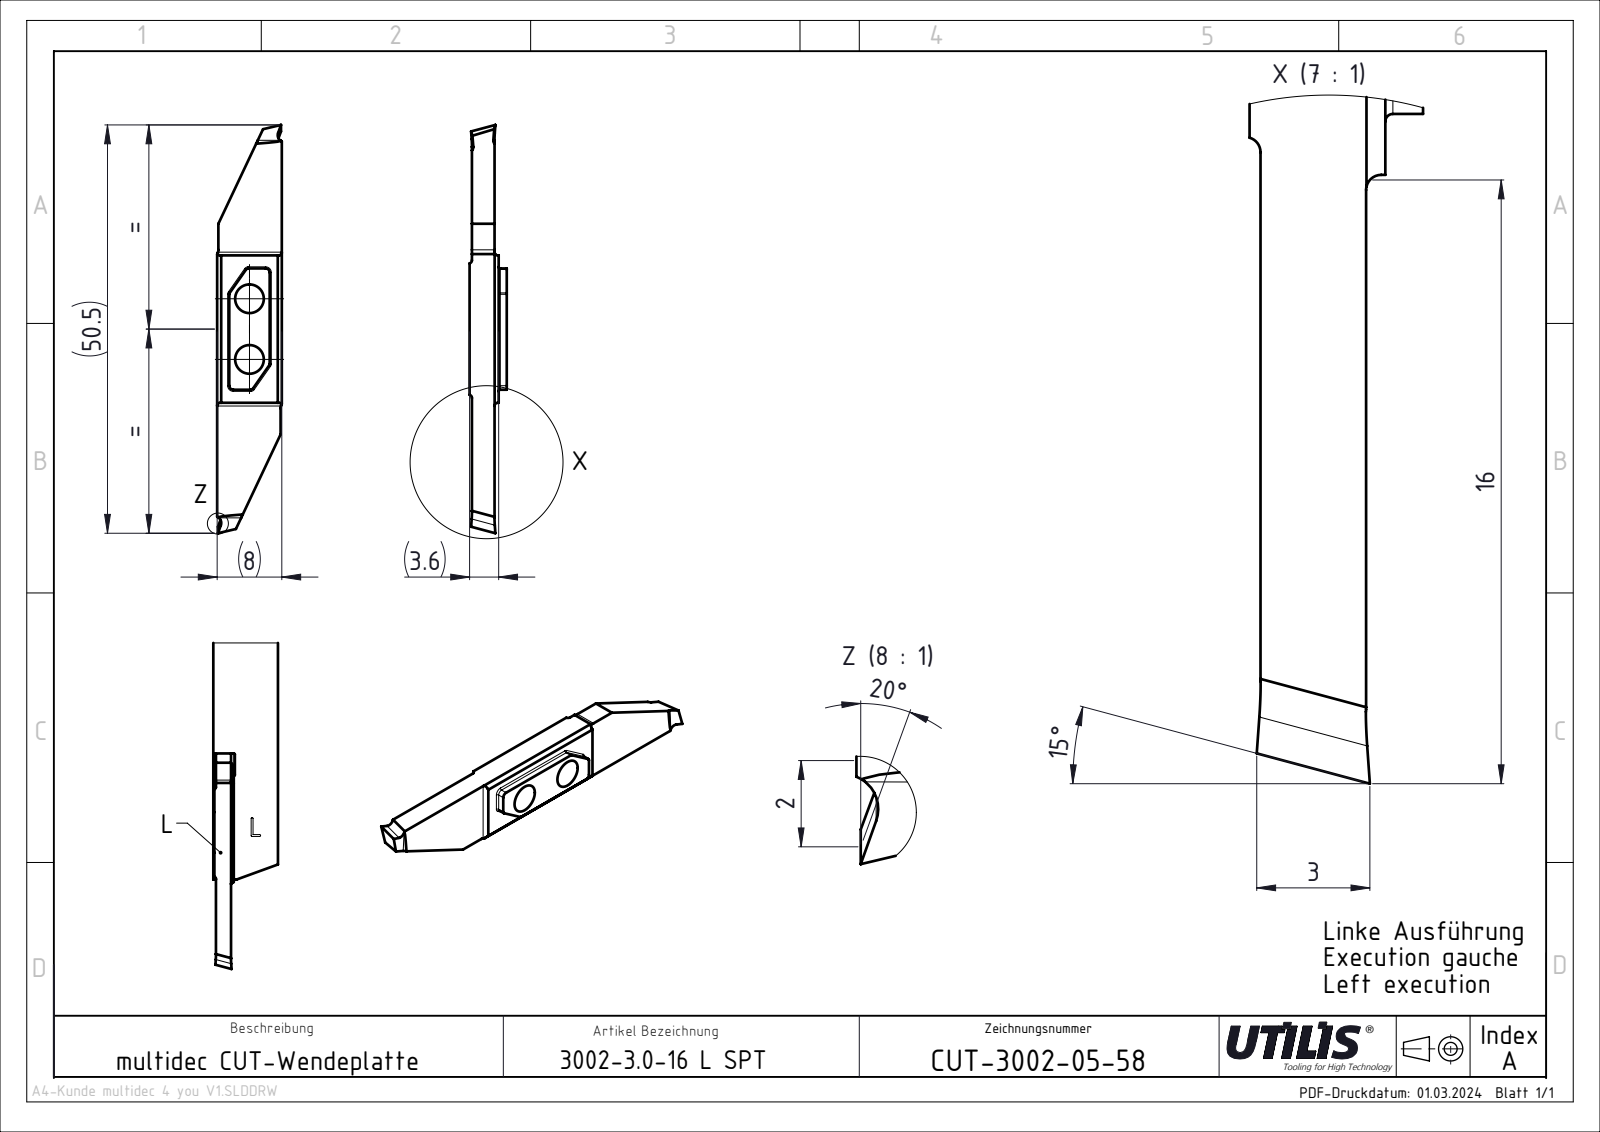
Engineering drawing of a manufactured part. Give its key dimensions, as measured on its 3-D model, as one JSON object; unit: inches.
{"part_name": "CUT-3002 SPT Slim_and_Deep; ASME Y14.5", "step_written_by": "SolidWorks 2023 SP4 || FormatWorks Professional (AP242_MANAGED_MODEL_BASED_3D_ENGINEERING_MIM_LF)", "units": "inches", "bodies": {"solids": 1, "faces": 32, "planar": 22, "cylindrical": 10, "other": 0}, "overall_size": [1.988, 0.315, 0.142], "volume_in3": 0.058, "surface_area_in2": 1.579, "round_holes": [[0.14, 2]], "partial_cylinders_radius": [[0.016, 4], [0.039, 2]], "face_to_face_distances": [0.11, 0.122, 0.142, 0.13, 0.02, 0.315, 0.712, 0.309, 0.303, 0.016], "hole_center_spacings": [0.295]}
